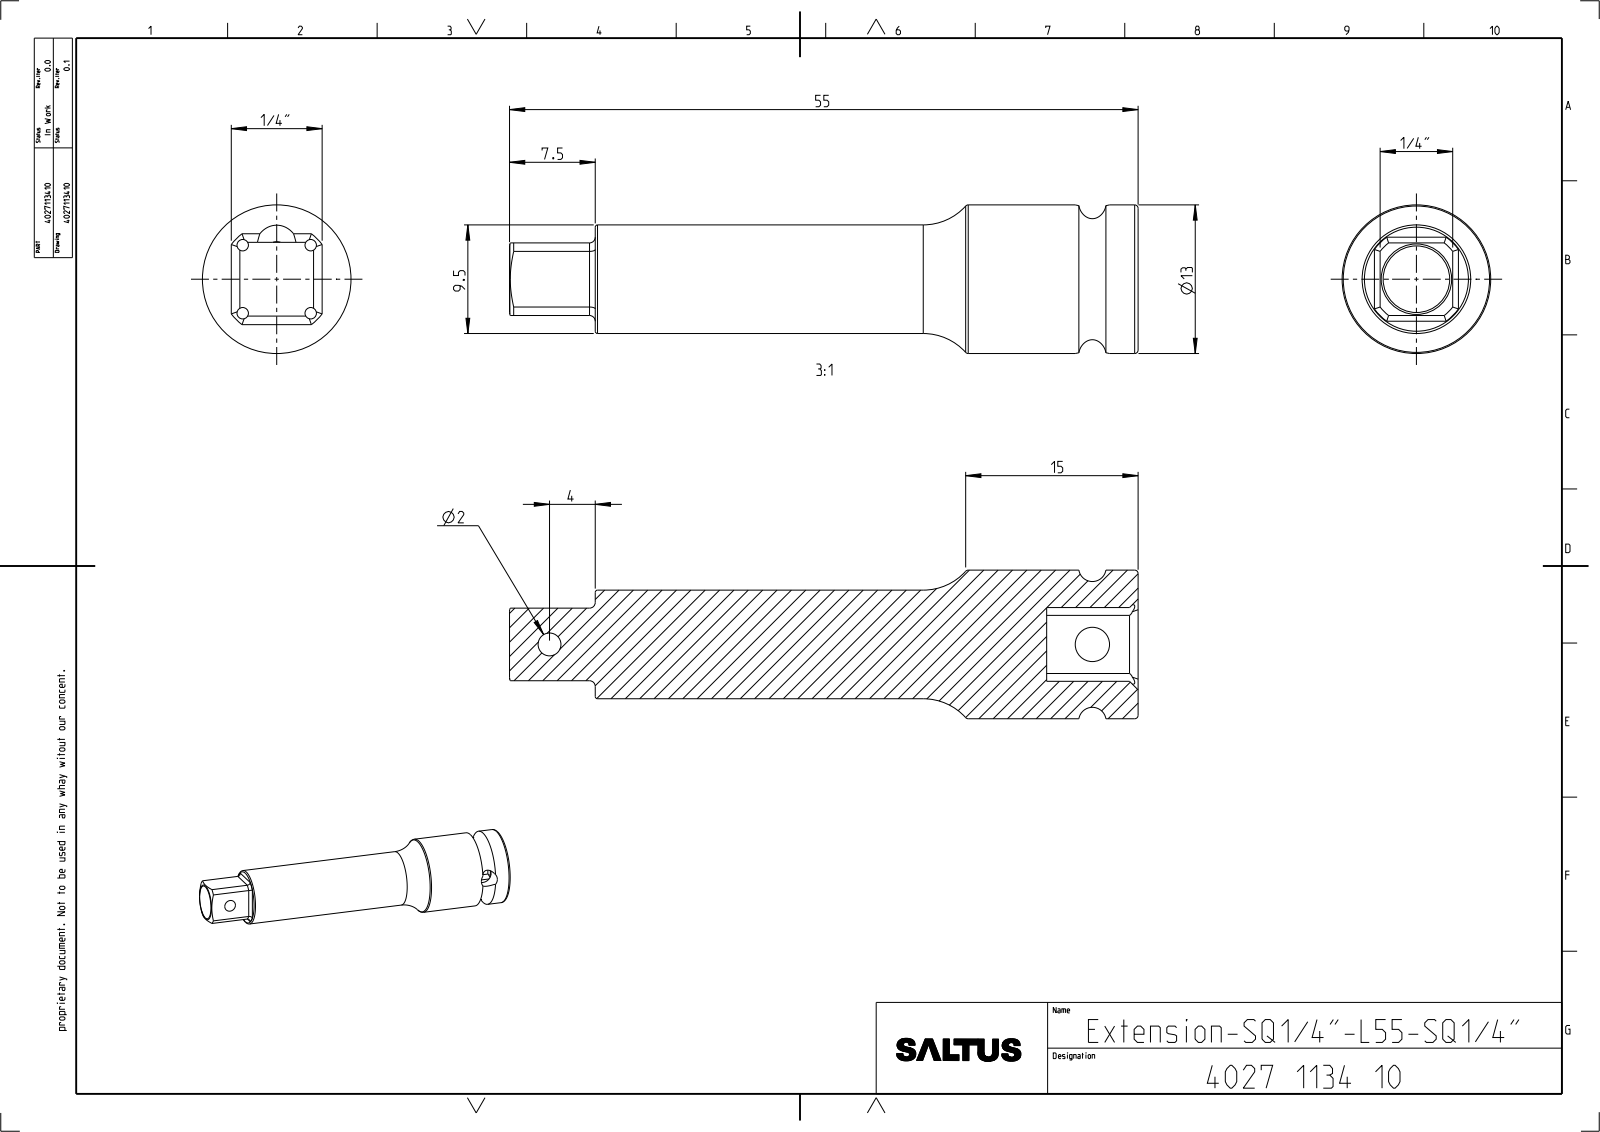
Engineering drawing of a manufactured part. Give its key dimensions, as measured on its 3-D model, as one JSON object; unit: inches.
{"part_name": "4027113410", "step_written_by": "CREO PARAMETRIC BY PTC INC, 2022414 (CONFIG_CONTROL_DESIGN)", "units": "inches", "bodies": {"solids": 1, "faces": 76, "planar": 17, "cylindrical": 29, "other": 30}, "overall_size": [2.165, 0.512, 0.512], "volume_in3": 0.255, "surface_area_in2": 3.519, "round_holes": [[0.039, 4], [0.079, 1], [0.118, 1]], "round_bosses_or_shafts": [[0.512, 1], [0.374, 1]], "partial_cylinders_radius": [[0.02, 4], [0.079, 1], [0.157, 1]], "face_to_face_distances": [0.252, 0.25, 0.254, 0.315, 2.165, 1.85, 1.87, 1.555, 0.295], "hole_center_spacings": [0.235, 0.332, 1.87]}
